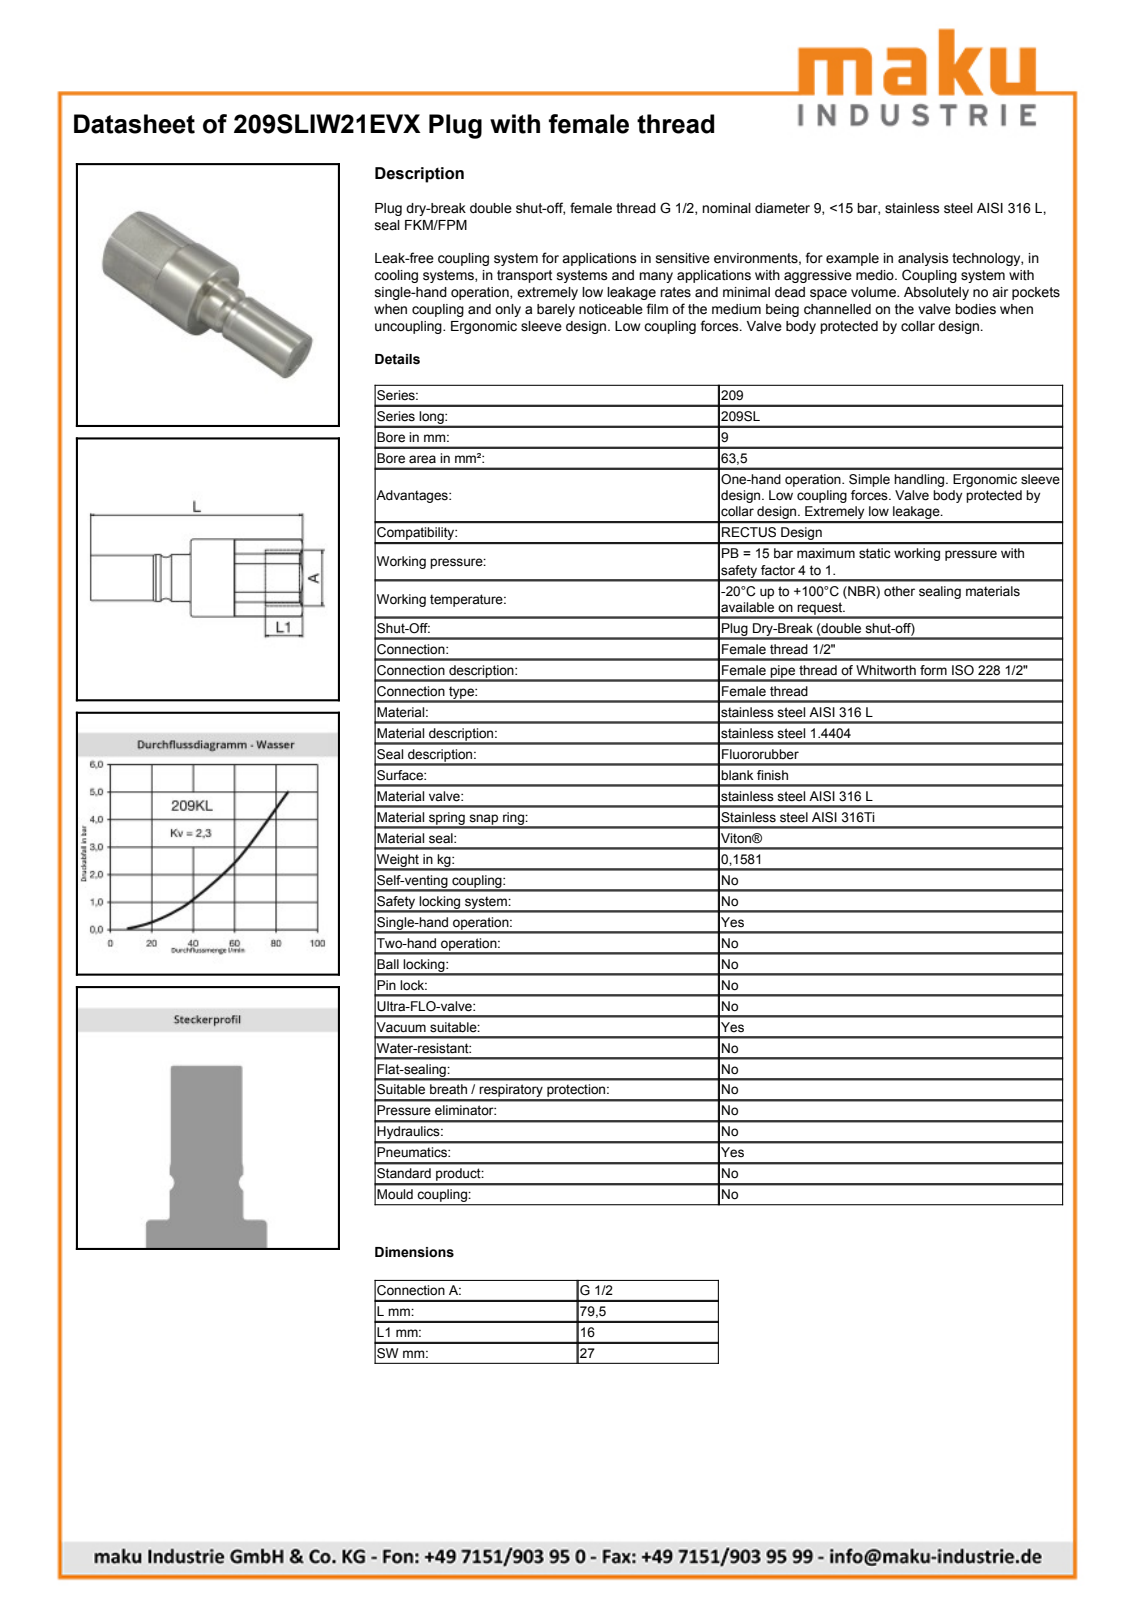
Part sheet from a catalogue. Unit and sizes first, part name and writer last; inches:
Units: inches
Overall size (bounding box): 3.126 × 1.142 × 1.142
Round holes (diameter × count): ⌀0.733 ×1, ⌀0.829 ×1, ⌀0.949 ×1, ⌀0.984 ×1, ⌀1.055 ×1
Round bosses / shafts (diameter × count): ⌀1.142 ×1, ⌀0.961 ×1, ⌀0.941 ×1, ⌀0.778 ×1, ⌀0.688 ×1, ⌀0.668 ×1
Main face-to-face distances: 1.097, 1.064, 1.063, 1.062, 1.65, 0.552, 1.476, 2.574, 3.126, 1.709
Volume: 1.867 in³ · Surface area: 15.48 in²
Bodies: 1 solid, 70 faces (27 planar, 19 cylindrical, 24 other)
Part name (STEP PRODUCT): D108682
STEP written by: Autodesk Inventor 2013 (AUTOMOTIVE_DESIGN)
